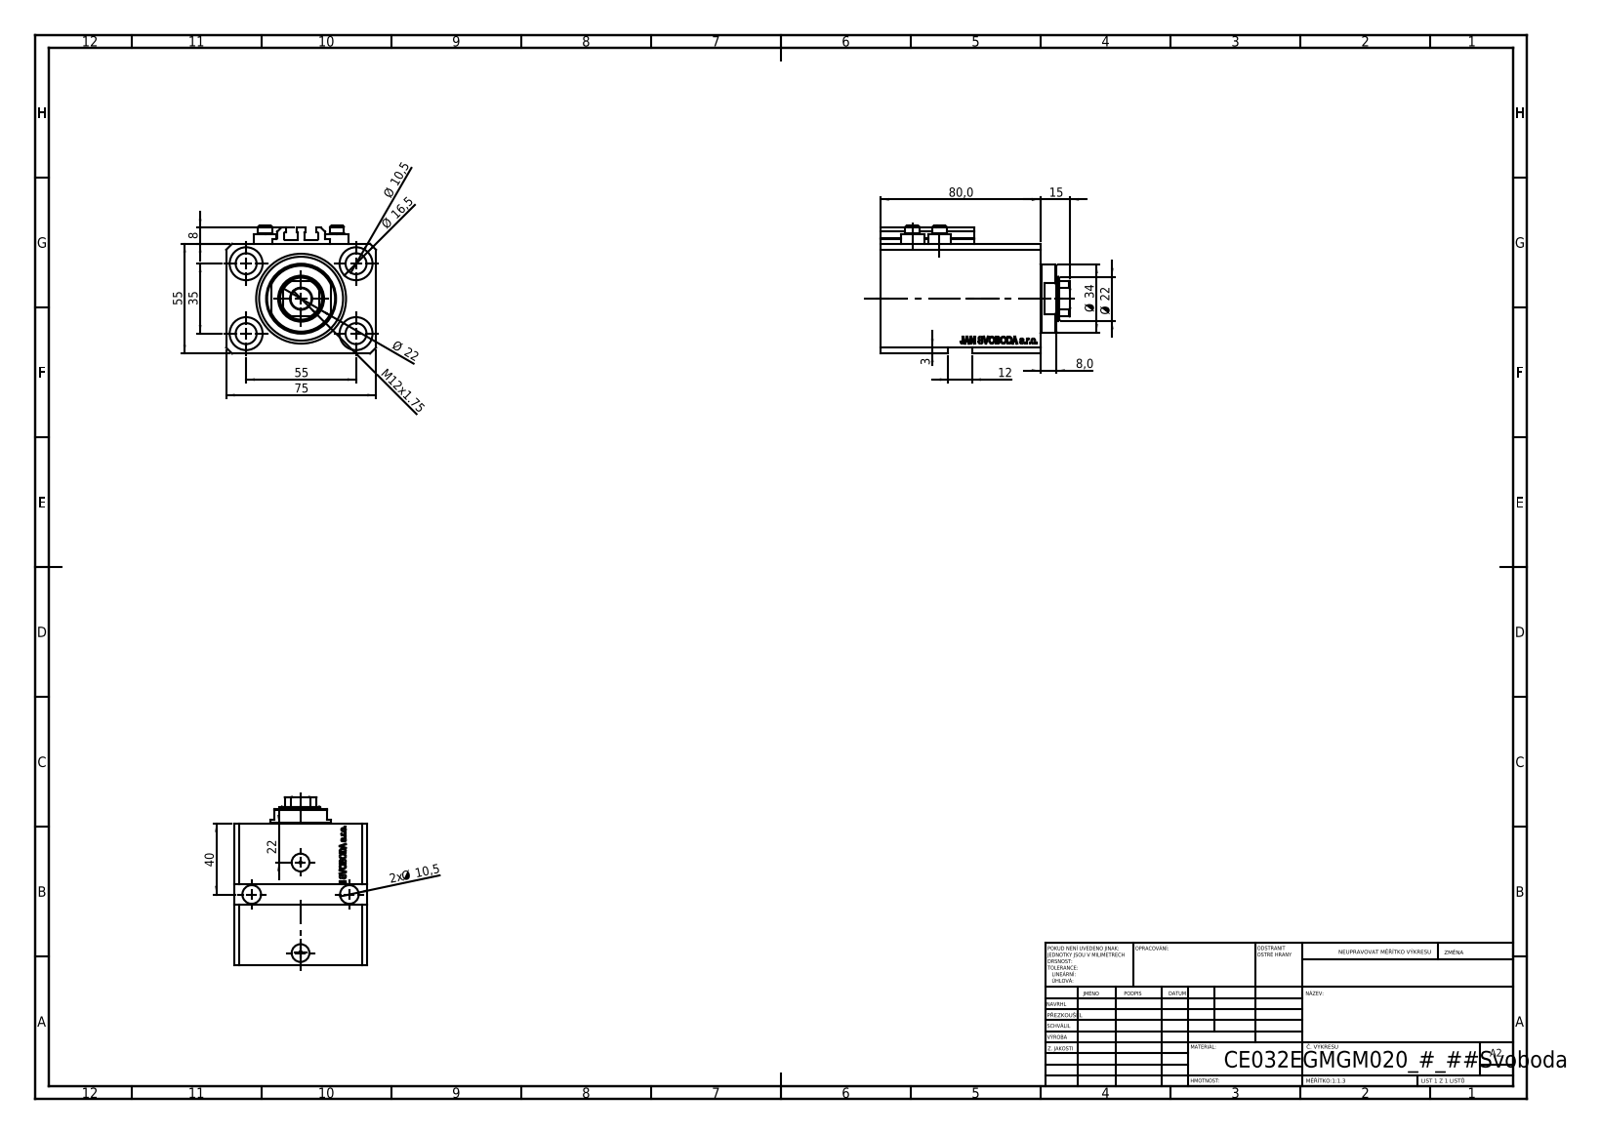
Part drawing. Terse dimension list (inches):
name: ALLEN BOLT V250CE; V250CE_C_VCP; V250CE_VC_E; V250CE_E_Body
written by: SolidWorks 2019 (CONFIG_CONTROL_DESIGN)
unit: in
bodies: 8 solids, 1064 faces (514 planar, 126 cylindrical, 424 other)
size: 3.74 × 2.953 × 2.52
volume: 17.32 in³; area: 115.4 in²
holes: 7× ⌀0.413, 4× ⌀0.049, 4× ⌀0.157, 4× ⌀0.65, 2× ⌀0.394, 2× ⌀0.518, 2× ⌀0.787, 1× ⌀0.866, 1× ⌀1.26, 1× ⌀1.772
bosses: 4× ⌀0.457, 4× ⌀0.276, 1× ⌀1.339
rounds: 10× R0.008, 1× R0.413
face distances: 2.165, 2.953, 0.591, 3.15, 2.559, 0.118, 2.169, 0.39, 2.76, 2.126
hole spacings: 1.283, 2.165, 0.535, 0.555, 0.783, 0.792, 1.016, 1.121
